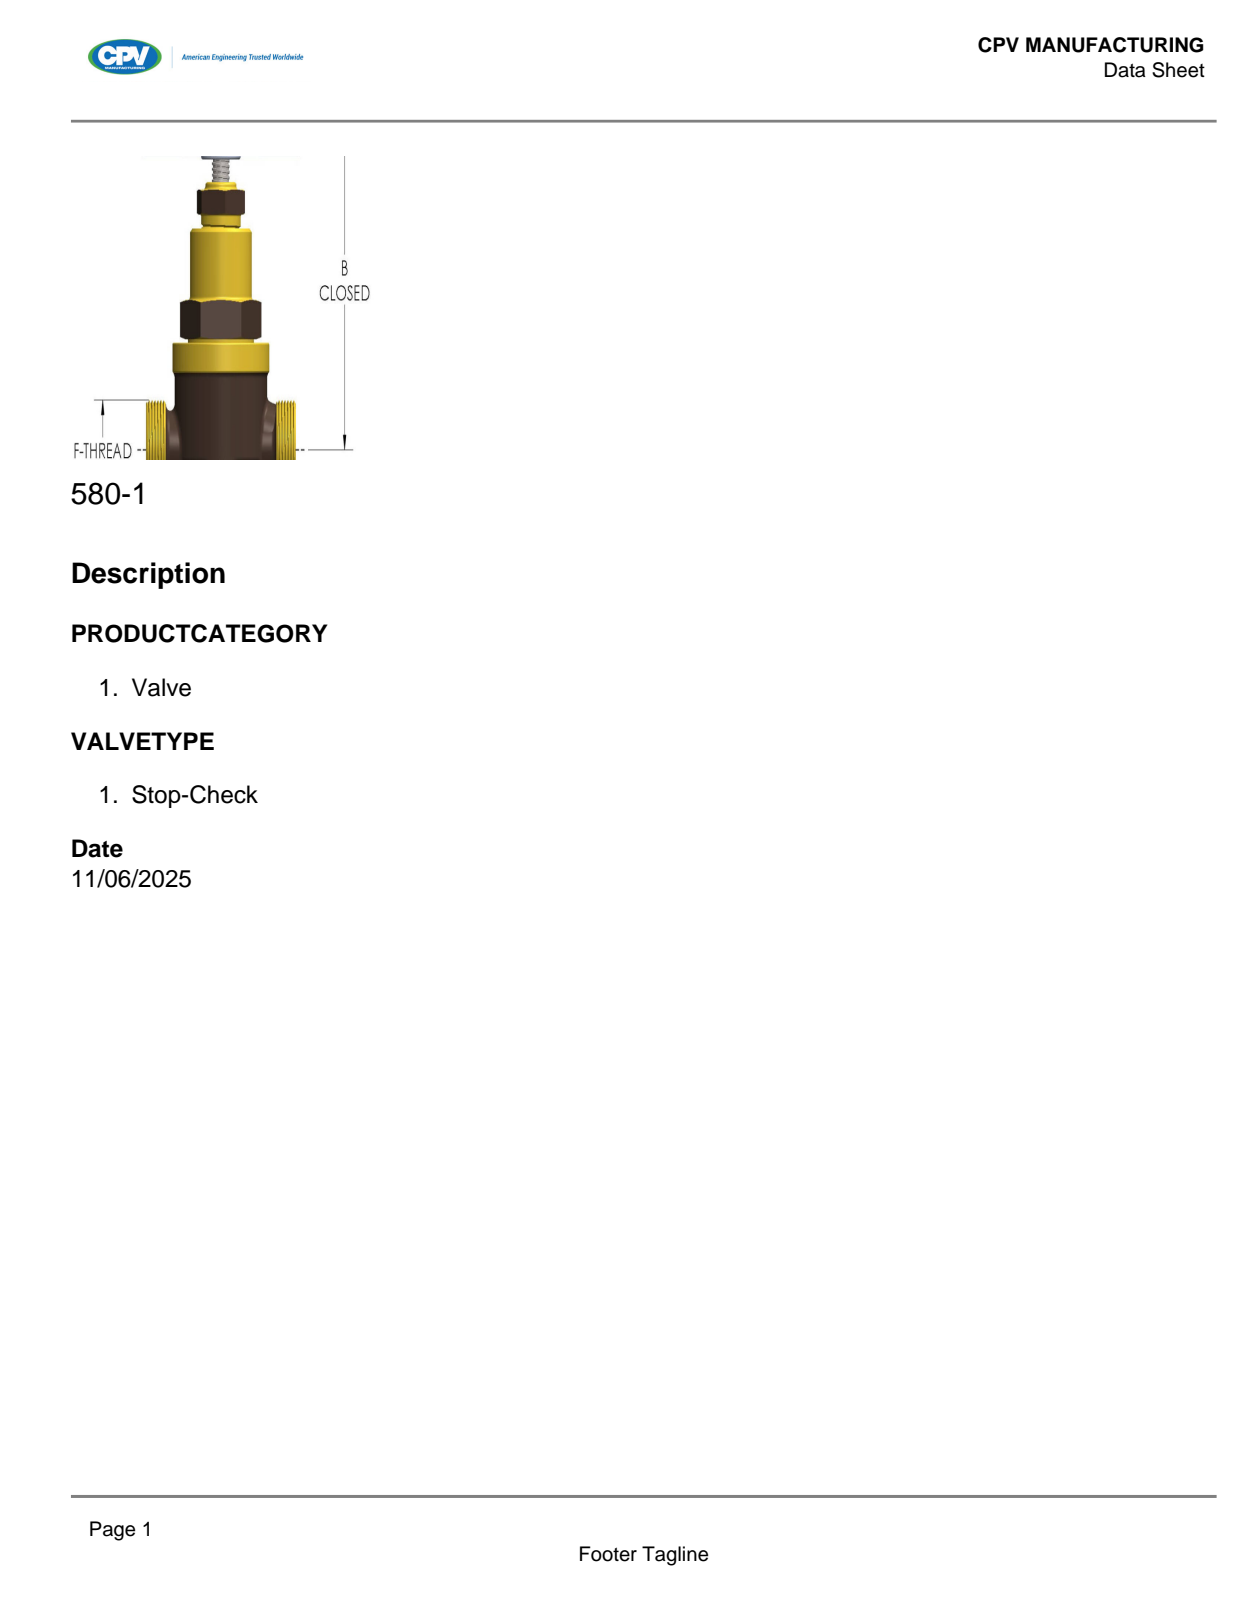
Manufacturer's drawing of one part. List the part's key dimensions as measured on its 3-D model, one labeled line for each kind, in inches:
Part name (STEP PRODUCT): 380-1
STEP written by: SolidWorks 2018 (AUTOMOTIVE_DESIGN)
Units: inches
Bodies: 3 solids, 636 faces (127 planar, 242 cylindrical, 267 other)
Overall size (bounding box): 5.101 × 3.499 × 3.499
Volume: 9.576 in³ · Surface area: 70.2 in²
Round holes (diameter × count): ⌀0.313 ×3, ⌀0.255 ×1, ⌀0.798 ×1, ⌀1.043 ×1, ⌀1.16 ×1, ⌀1.25 ×1, ⌀1.375 ×1
Round bosses / shafts (diameter × count): ⌀1.938 ×1, ⌀1.813 ×1, ⌀1.373 ×1, ⌀1.187 ×1, ⌀1.183 ×1, ⌀1.135 ×1, ⌀1.125 ×1, ⌀1.063 ×1
Partial cylindrical surfaces — rounded edges, fillets, slot ends (radius × count): R0.13 ×24, R0.005 ×16, R0.06 ×16, R0.375 ×3, R0.253 ×1, R0.54 ×1, R0.866 ×1, R0.901 ×1
Main face-to-face distances: 0.31, 1.78, 1.5, 0.19, 0.414, 1.365, 0.13, 3.374, 0.25, 1.25
Hole centre spacings: 0.874
